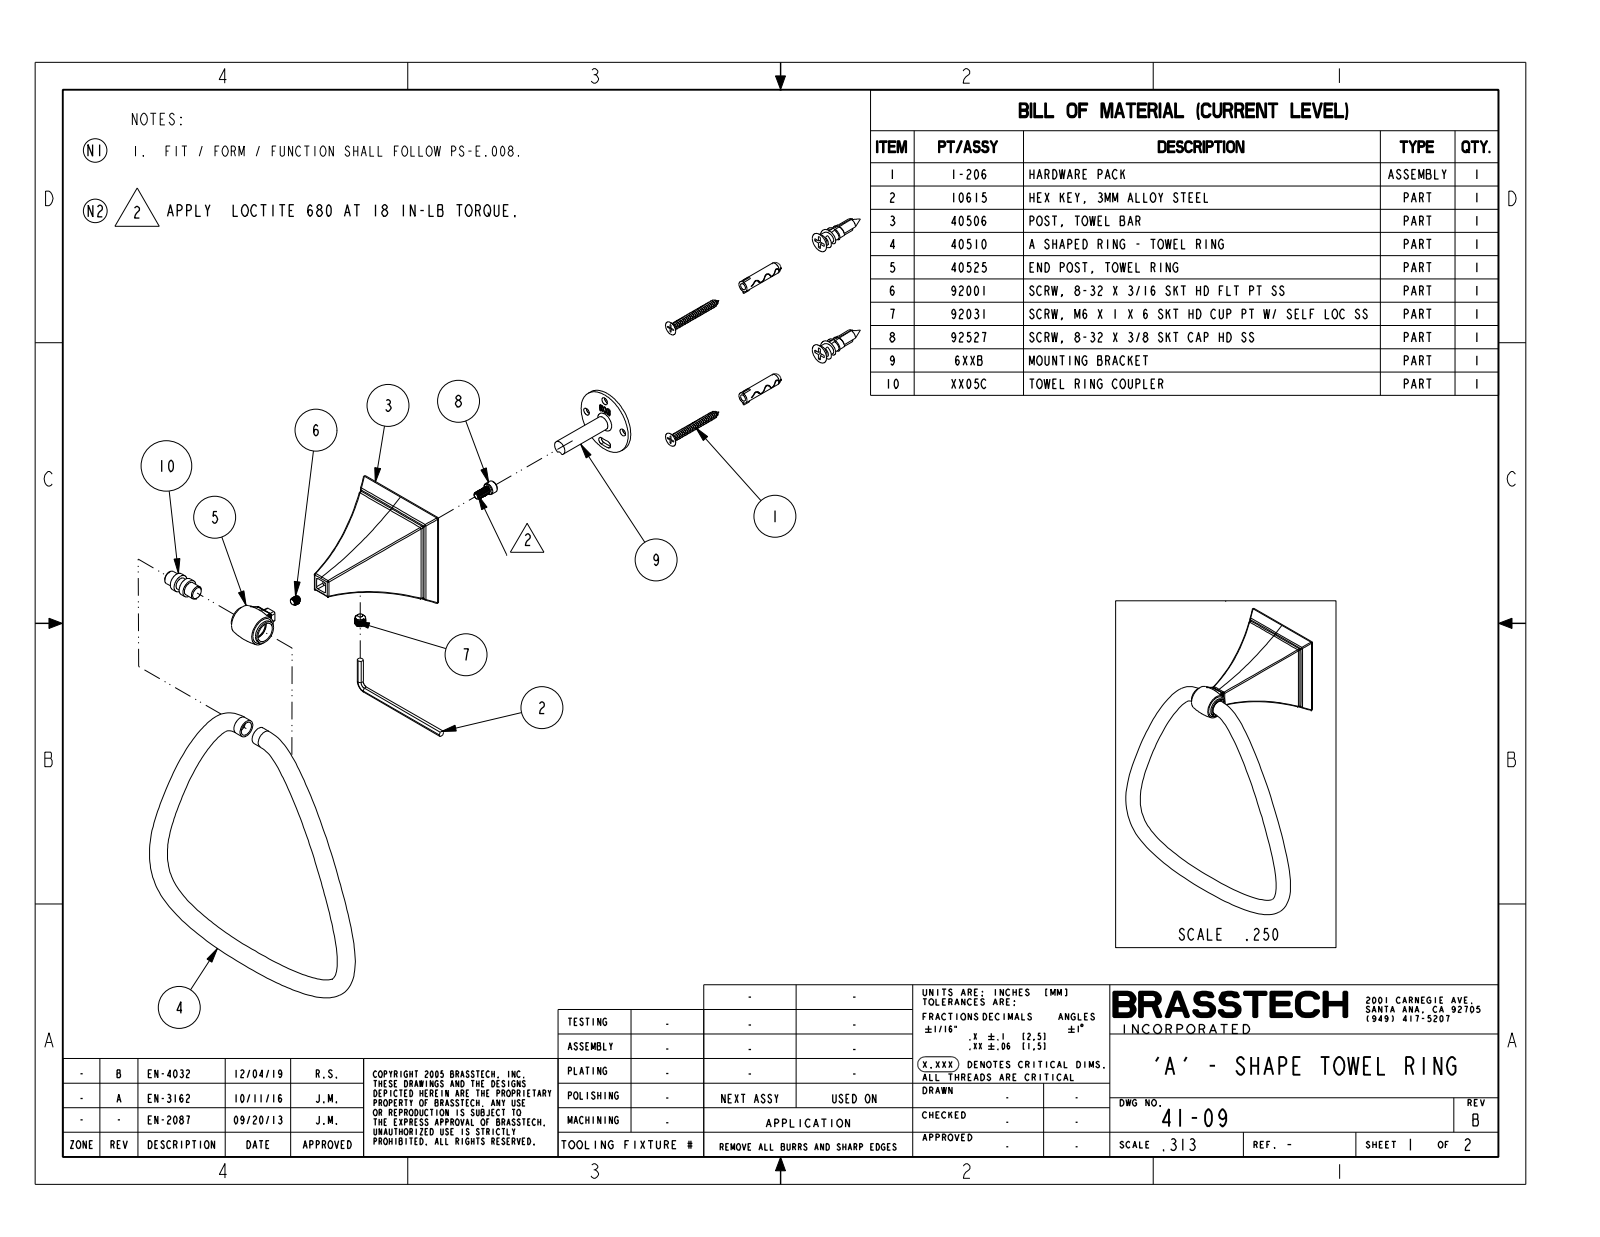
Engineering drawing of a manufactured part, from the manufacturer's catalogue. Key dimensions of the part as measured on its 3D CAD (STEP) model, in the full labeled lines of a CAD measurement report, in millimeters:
Part name (STEP PRODUCT): 4905
STEP written by: PRO/ENGINEER BY PARAMETRIC TECHNOLOGY CORPORATION, 2012230 (CONFIG_CONTROL_DESIGN)
Units: millimetres
Bodies: 0 solids, 248 faces (32 planar, 59 cylindrical, 157 other)
Overall size (bounding box): 190 × 158.3 × 82.8
Round holes (diameter × count): ⌀4.3 ×3, ⌀5 ×1, ⌀6.4 ×1, ⌀11.3 ×1
Round bosses / shafts (diameter × count): ⌀37.1 ×1, ⌀13.2 ×1, ⌀12.3 ×1, ⌀8 ×1
Partial cylindrical surfaces — rounded edges, fillets, slot ends (radius × count): R0.8 ×4, R1 ×4, R2 ×4, R5.1 ×4, R2.2 ×2, R4.1 ×2, R30.8 ×1, R45.4 ×1
Main face-to-face distances: 2, 26.2, 24.1, 58.4, 21.2, 37.2, 19.2, 39.2, 18, 16
Hole centre spacings: 20.2, 28.6
